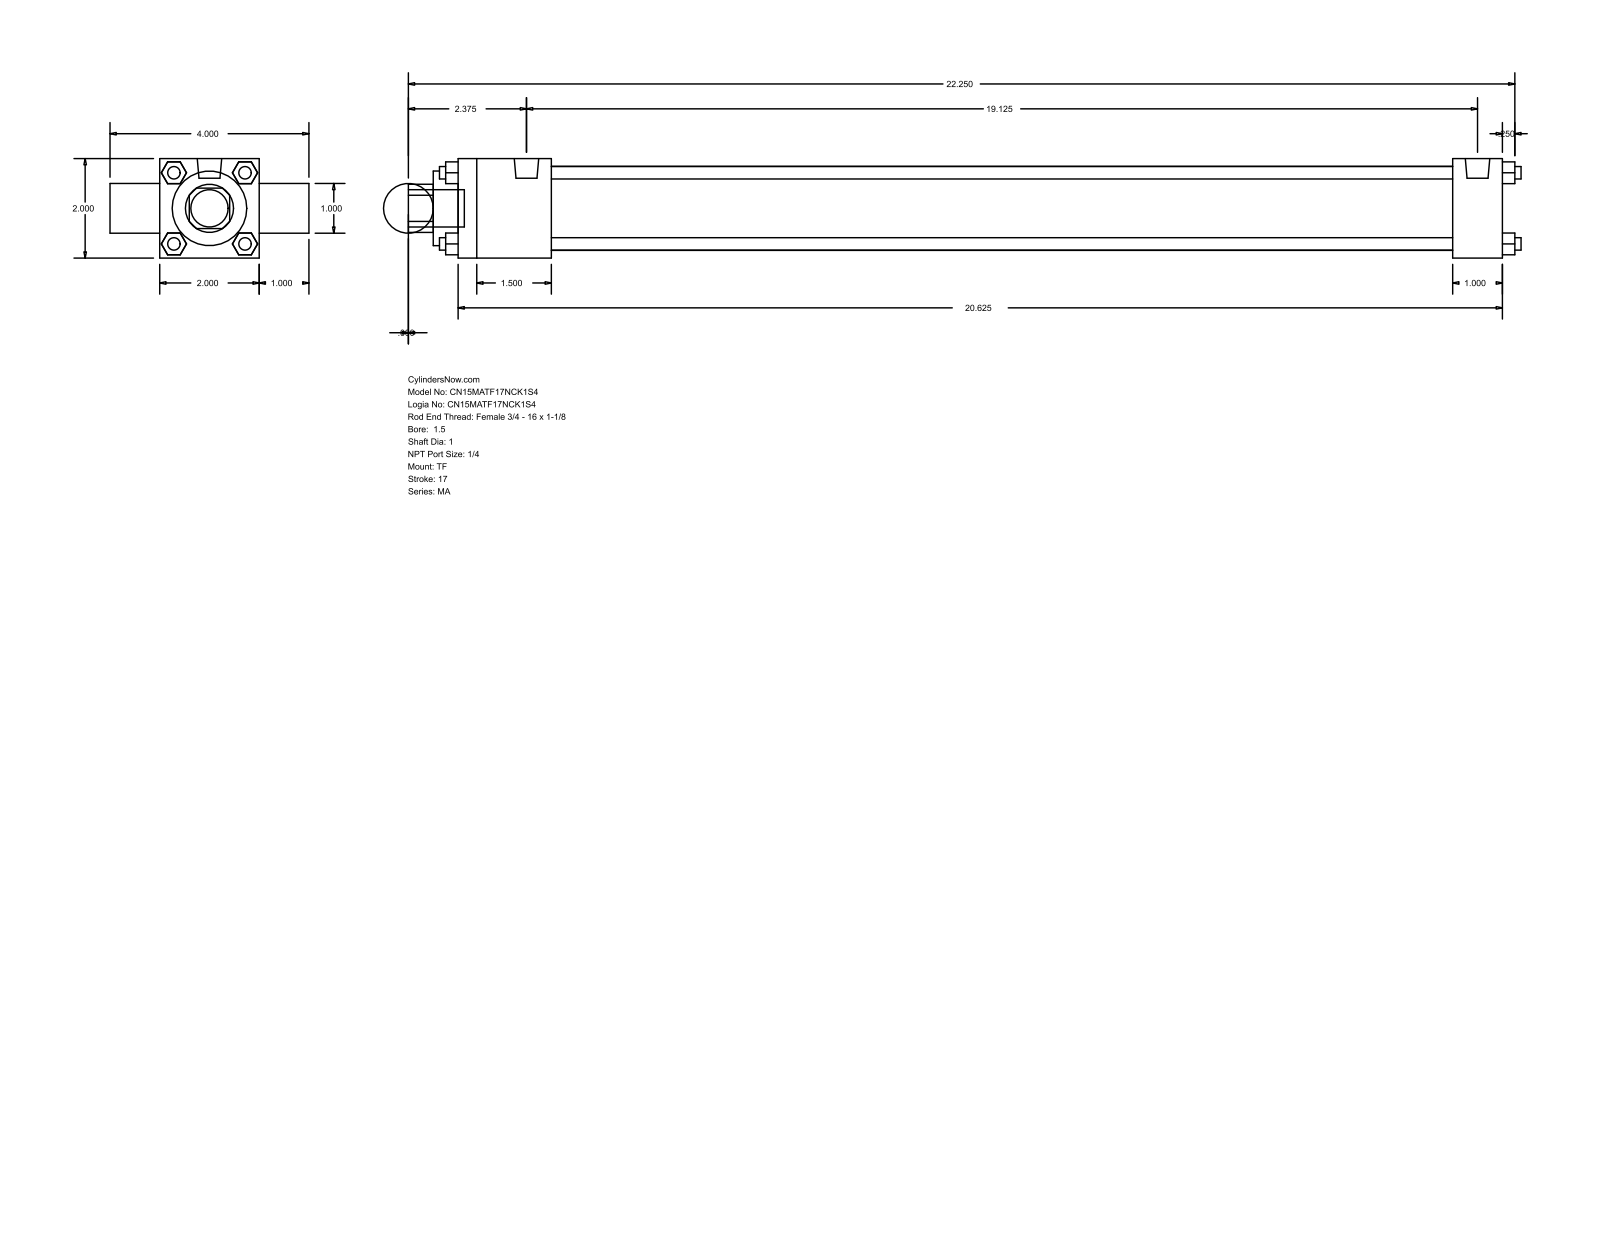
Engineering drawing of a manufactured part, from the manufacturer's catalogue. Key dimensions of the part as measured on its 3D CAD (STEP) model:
Part name (STEP PRODUCT): MA_TF__0150_1
STEP written by: GSSL Pune (CONFIG_CONTROL_DESIGN)
Units: millimetres
Bodies: 0 solids, 120 faces (92 planar, 28 cylindrical, 0 other)
Overall size (bounding box): 568.33 × 101.6 × 50.8
Round holes (diameter × count): ⌀25.4 ×2, ⌀38.1 ×1, ⌀42.93 ×1
Round bosses / shafts (diameter × count): ⌀6.35 ×4, ⌀7.94 ×3, ⌀12.49 ×2, ⌀19.05 ×1
Partial cylindrical surfaces — rounded edges, fillets, slot ends (radius × count): R12.29 ×1
Main face-to-face distances: 50.8, 25.4, 533.4, 76.2, 6.35, 47.63, 508, 460.37, 485.77, 546.1
